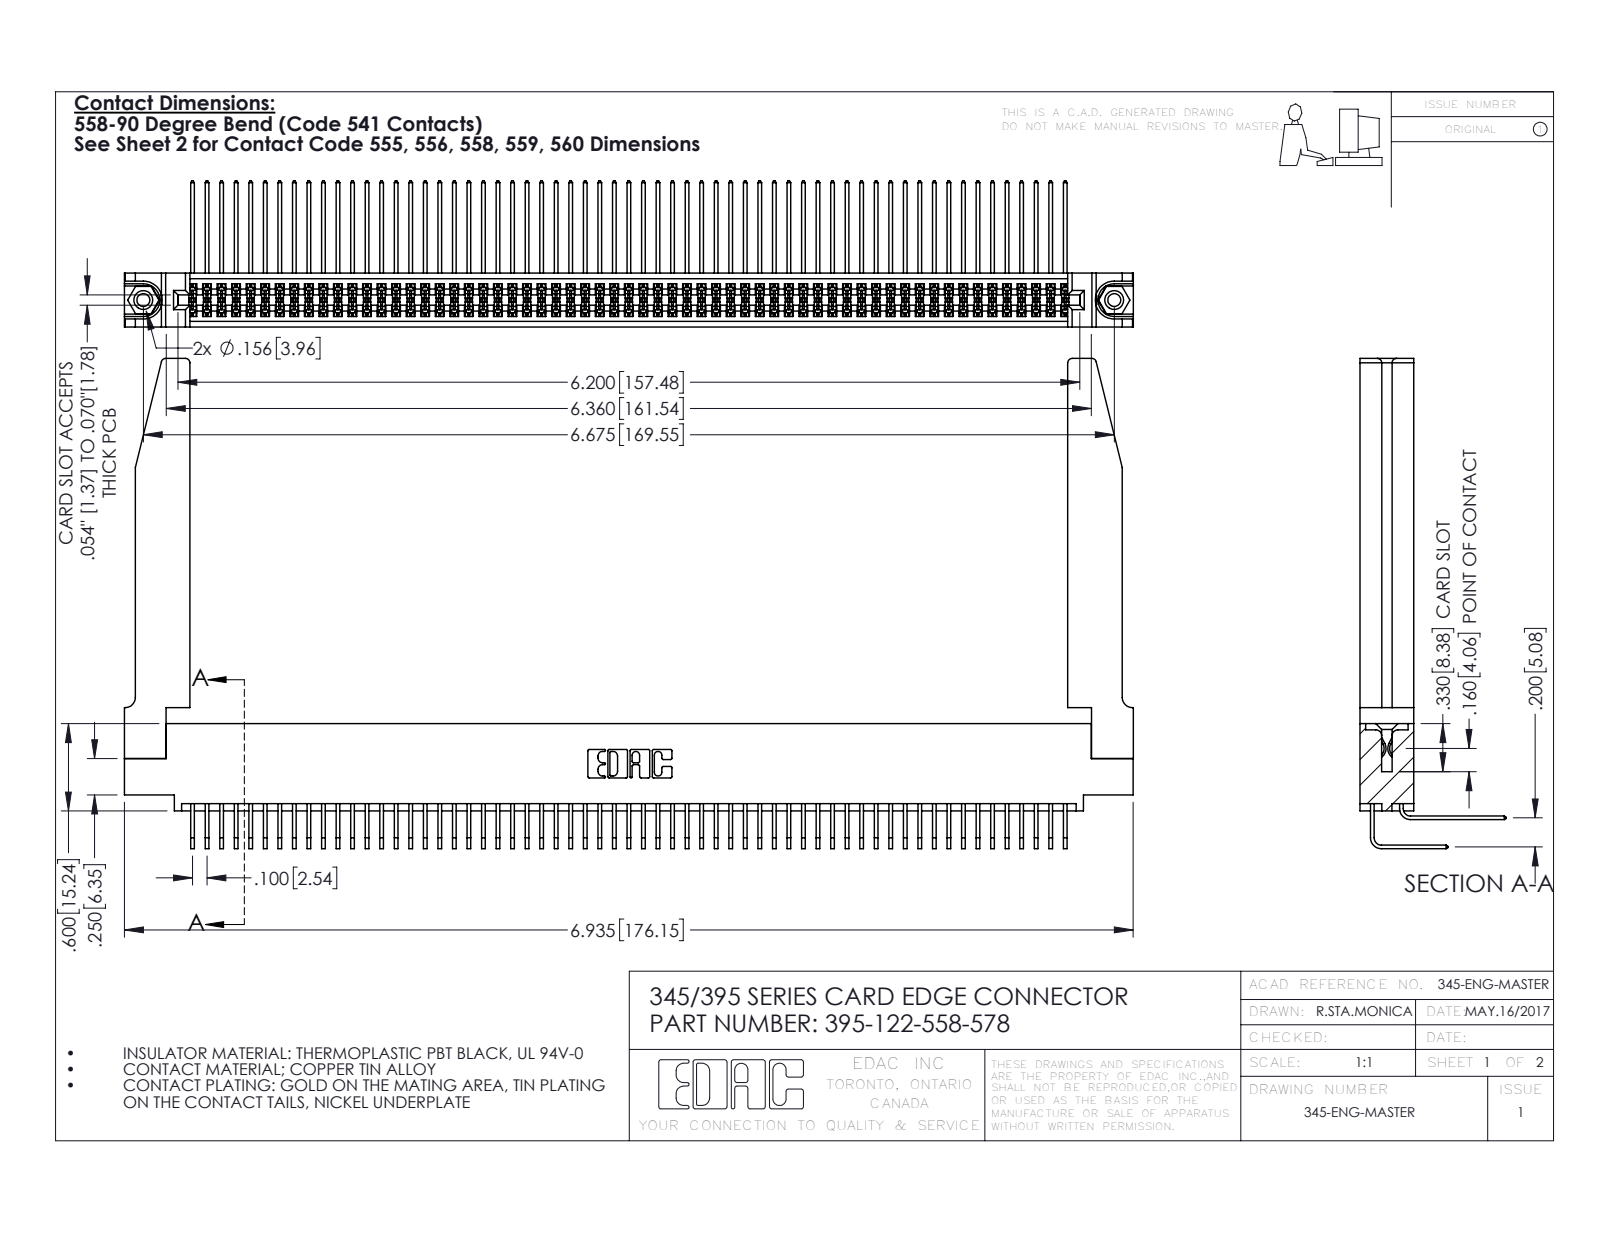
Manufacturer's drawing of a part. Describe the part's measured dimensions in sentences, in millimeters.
The part is named "395-122-558-578; 345 Part_0.110 Offset - 0.156 Dia-TH; 345-250-001_345-250-001-102; 345-292-001_558 Tail - 2 (+2 more)". Its 3-D file was written by "SolidWorks 2016 (CONFIG_CONTROL_DESIGN)". It is 127 solids with 6708 faces: 4496 planar, 2160 cylindrical and 52 other. Overall it measures 176.2 by 85.6 by 25.5 millimeters. Its volume is 25 690 cubic millimeters and its surface area 37 100 square millimeters. Round holes: 2 of diameter 2.3, 2 of diameter 3.2, 2 of diameter 4, 1 of diameter 1.6. Round bosses or shafts: 2 of diameter 3.9. Partial cylindrical surfaces (rounded edges, fillets, slot ends): 183 of radius 0.2, 22 of radius 0.3, 8 of radius 0.8, 6 of radius 0.2, 6 of radius 0.8, 3 of radius 0.7, 2 of radius 0.4, 2 of radius 0.5. The main face-to-face distances are 1.8, 7.6, 9.4, 5.1, 2.5, 6.9, 0.6, 5.7, 0.6, 4.4. The hole center spacings are 6.9, 163.6, 169.5.
